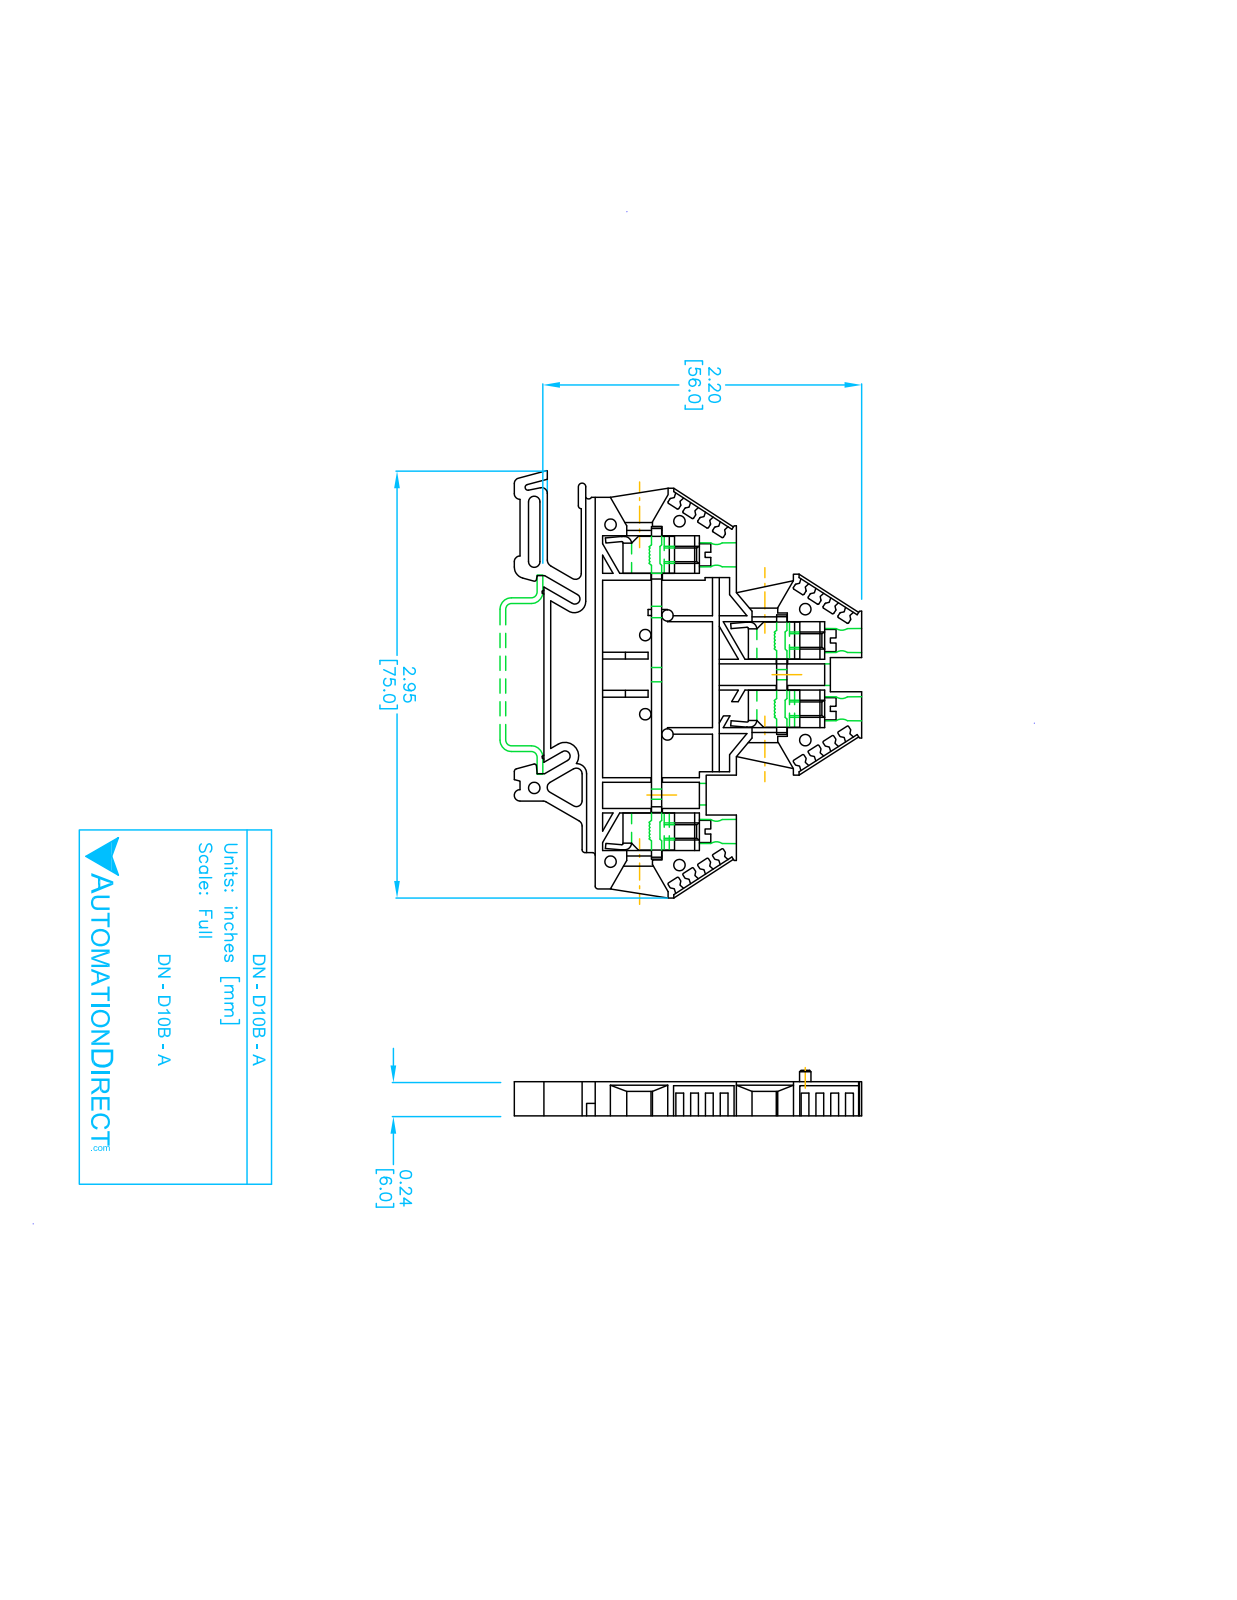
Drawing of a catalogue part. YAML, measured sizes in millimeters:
part_name: "DN-D10B-A"
step_written_by: "SolidWorks 2017 (AUTOMOTIVE_DESIGN)"
units: millimeters
bodies: {solids: 1, faces: 402, planar: 261, cylindrical: 141, other: 0}
overall_size: [75.1, 61, 6]
volume: 14700
surface_area: 9581
round_holes:
  - {diameter: 4.2, count: 4}
  - {diameter: 2, count: 1}
round_bosses_or_shafts:
  - {diameter: 3.7, count: 4}
partial_cylinders:
  - {radius: 0.2, count: 64}
  - {radius: 1, count: 13}
  - {radius: 0.5, count: 6}
  - {radius: 0.3, count: 2}
  - {radius: 0.9, count: 2}
  - {radius: 1.9, count: 2}
  - {radius: 2, count: 2}
  - {radius: 0.1, count: 1}
face_to_face_distances: [6, 2, 4, 9, 1.5, 0.6, 0.8, 1.2, 24.8, 1.8]
hole_center_spacings: [12, 15.1, 21.5, 27.1, 33.6, 48.6]
